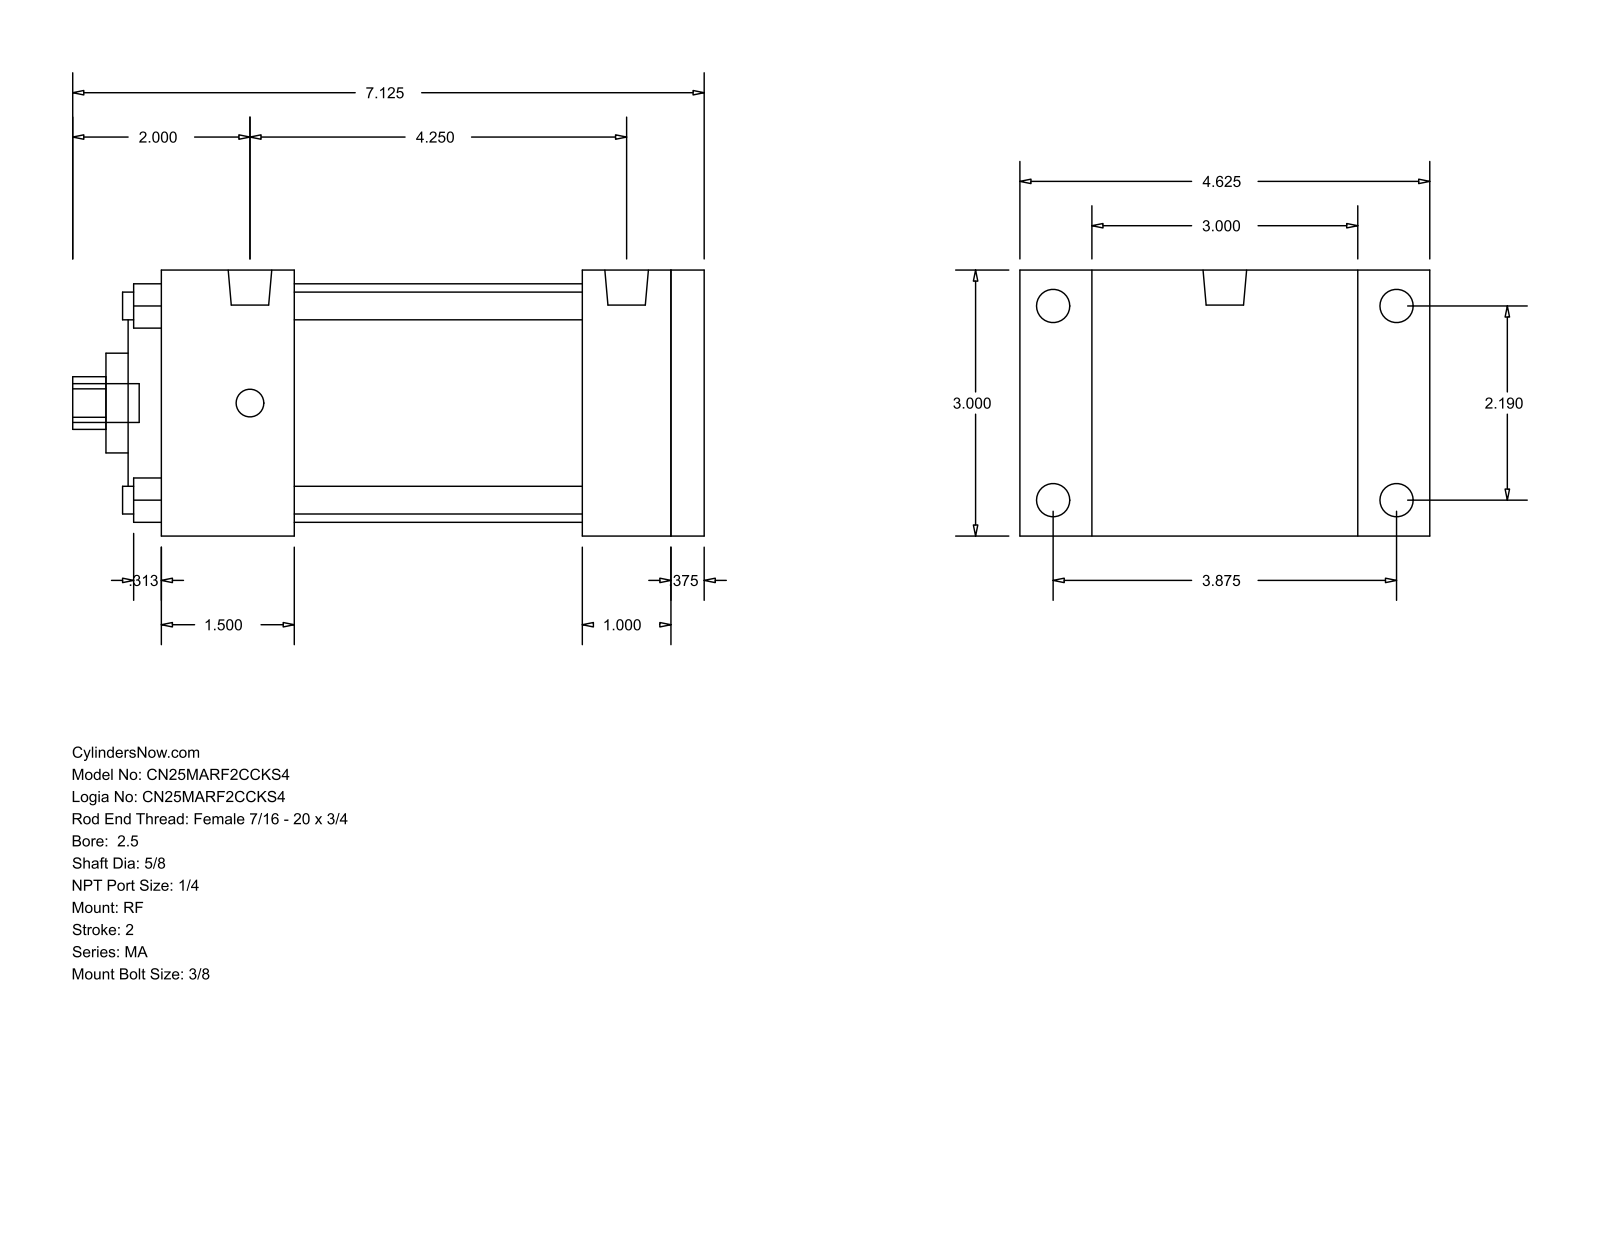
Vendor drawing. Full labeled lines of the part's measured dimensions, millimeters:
Part name (STEP PRODUCT): MA_RF__0250_0.625
STEP written by: GSSL Pune (CONFIG_CONTROL_DESIGN)
Units: millimetres
Bodies: 0 solids, 94 faces (65 planar, 29 cylindrical, 0 other)
Overall size (bounding box): 180.97 × 117.47 × 76.2
Round holes (diameter × count): ⌀7.94 ×4, ⌀15.88 ×1, ⌀28.57 ×1, ⌀50.8 ×1, ⌀68.33 ×1
Round bosses / shafts (diameter × count): ⌀9.53 ×4, ⌀7.94 ×4, ⌀12.49 ×2, ⌀11.11 ×1
Partial cylindrical surfaces — rounded edges, fillets, slot ends (radius × count): R7.54 ×1
Main face-to-face distances: 76.2, 155.57, 9.52, 146.05, 25.4, 38.1, 120.65, 82.55, 107.95, 117.47
Hole centre spacings: 39.33, 55.62, 78.66
